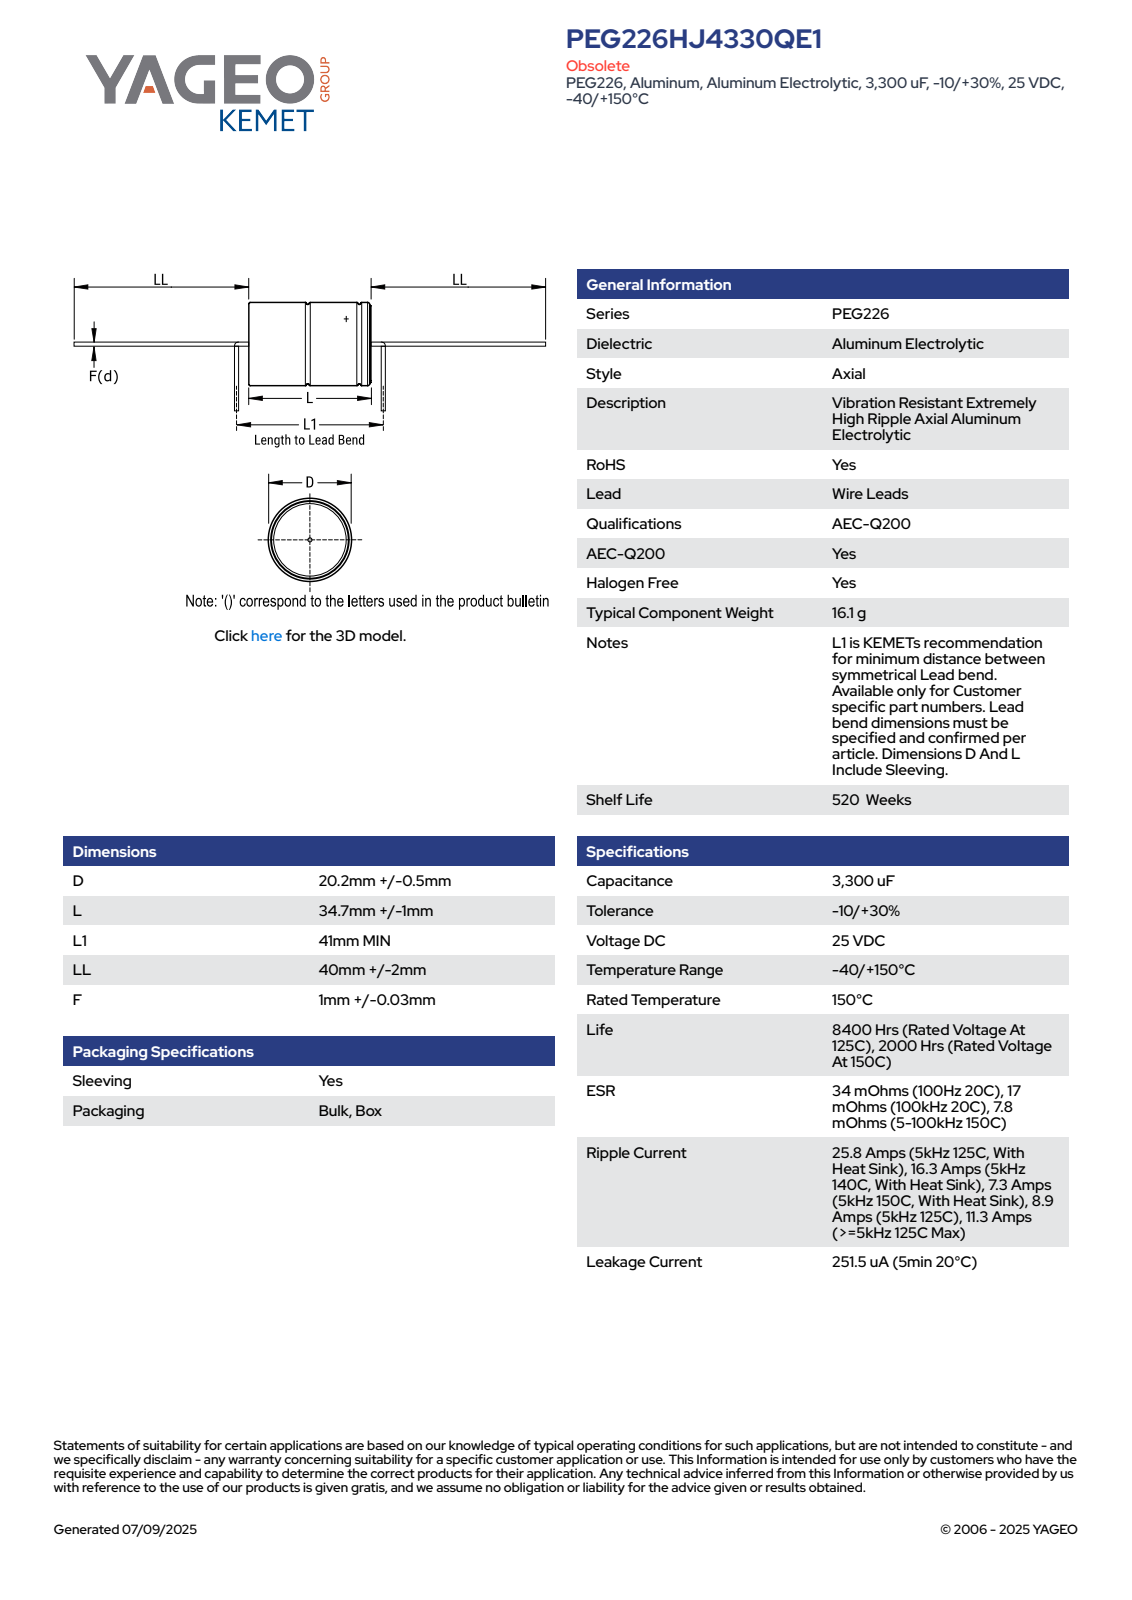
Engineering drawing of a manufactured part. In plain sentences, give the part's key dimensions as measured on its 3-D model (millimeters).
The part is named "CAA_PEG220_20X35_D20.7L35.7LL42F1.03". Its 3-D file was written by "SolidWorks 2014 (AUTOMOTIVE_DESIGN)". It is 1 solid with 99 faces: 27 planar, 29 cylindrical and 43 other. Overall it measures 119.7 by 20.7 by 20.7 millimeters. Its volume is 11 770 cubic millimeters and its surface area 3 336 square millimeters. Round holes: 1 of diameter 19.7. Round bosses or shafts: 1 of diameter 20.7, 1 of diameter 20.2, 1 of diameter 1.03. Partial cylindrical surfaces (rounded edges, fillets, slot ends): 1 of radius 10.34. The main face-to-face distances are 34.7, 35.7, 1, 42, 77.7, 76.7, 119.7, 43.
